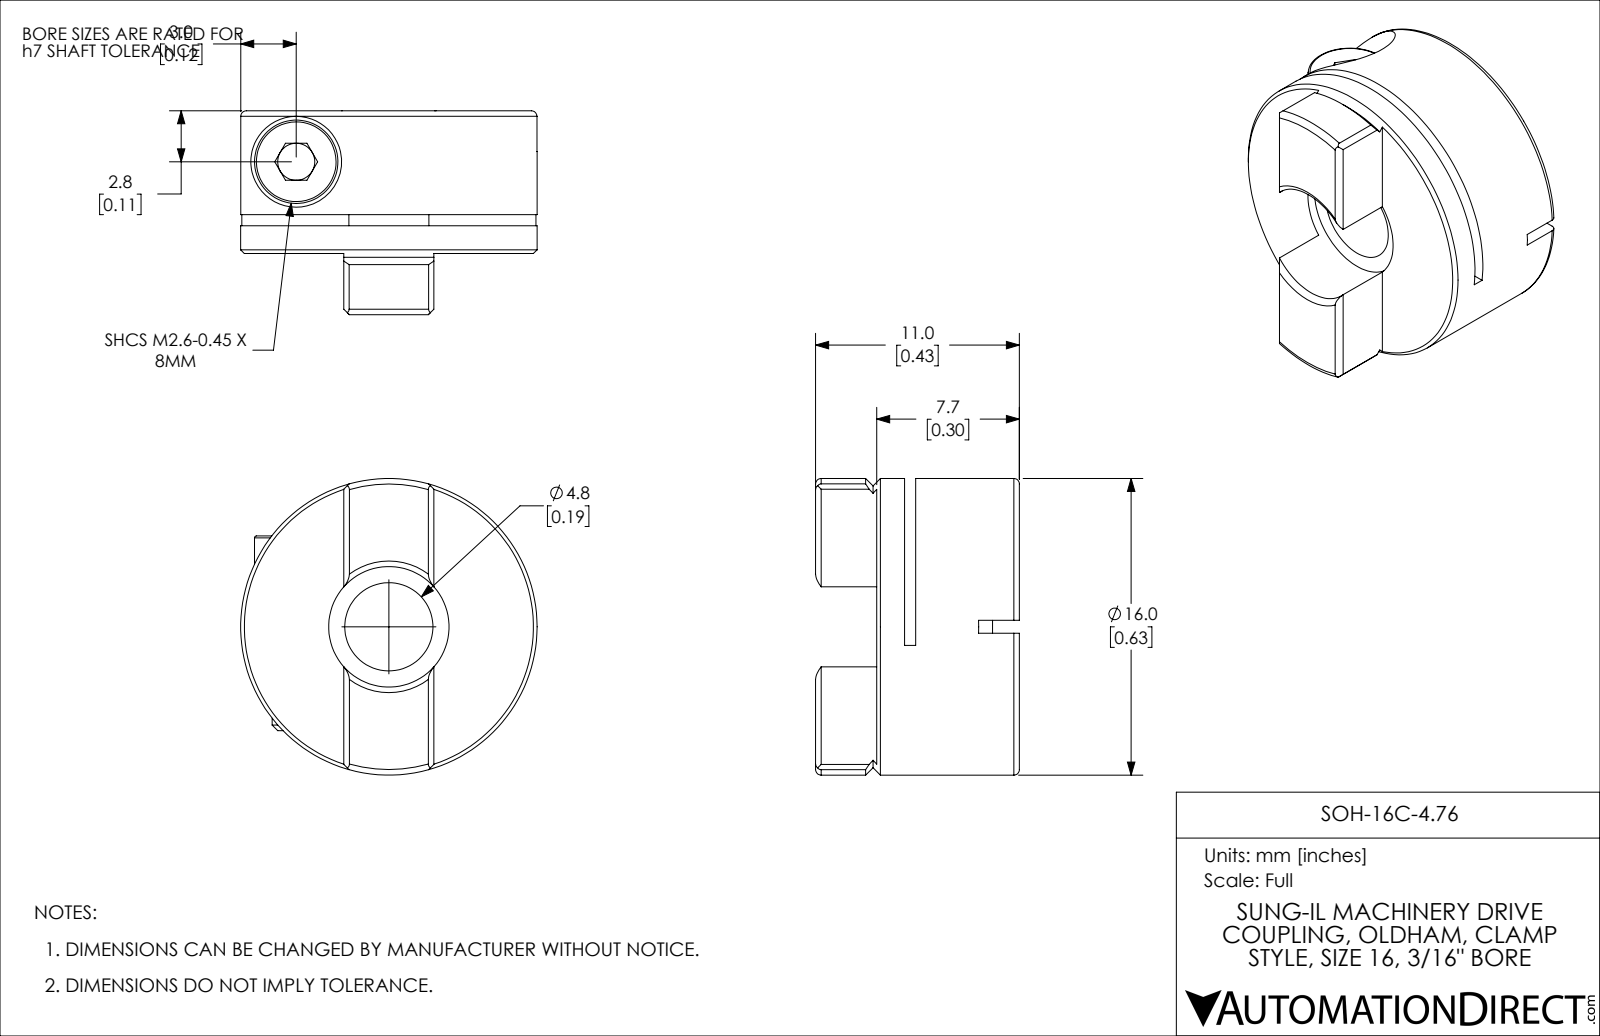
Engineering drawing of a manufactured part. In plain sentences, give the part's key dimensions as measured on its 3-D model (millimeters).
The part is named "SOH-16C-4". Its 3-D file was written by "SolidWorks 2021 (CONFIG_CONTROL_DESIGN)". It is 2 solids with 93 faces: 44 planar, 25 cylindrical and 24 other. Overall it measures 16 by 16 by 11 millimeters. Its volume is 1 465 cubic millimeters and its surface area 1 500 square millimeters. Round holes: 1 of diameter 2, 1 of diameter 2.05, 1 of diameter 2.8, 1 of diameter 4, 1 of diameter 4.9, 1 of diameter 6.5. Round bosses or shafts: 1 of diameter 16, 1 of diameter 4.5, 1 of diameter 2.6. Partial cylindrical surfaces (rounded edges, fillets, slot ends): 1 of radius 22.5. The main face-to-face distances are 7.7, 6.2, 1.5, 5.6, 0.6, 2.1, 0.7, 4.8, 11, 5.4.
